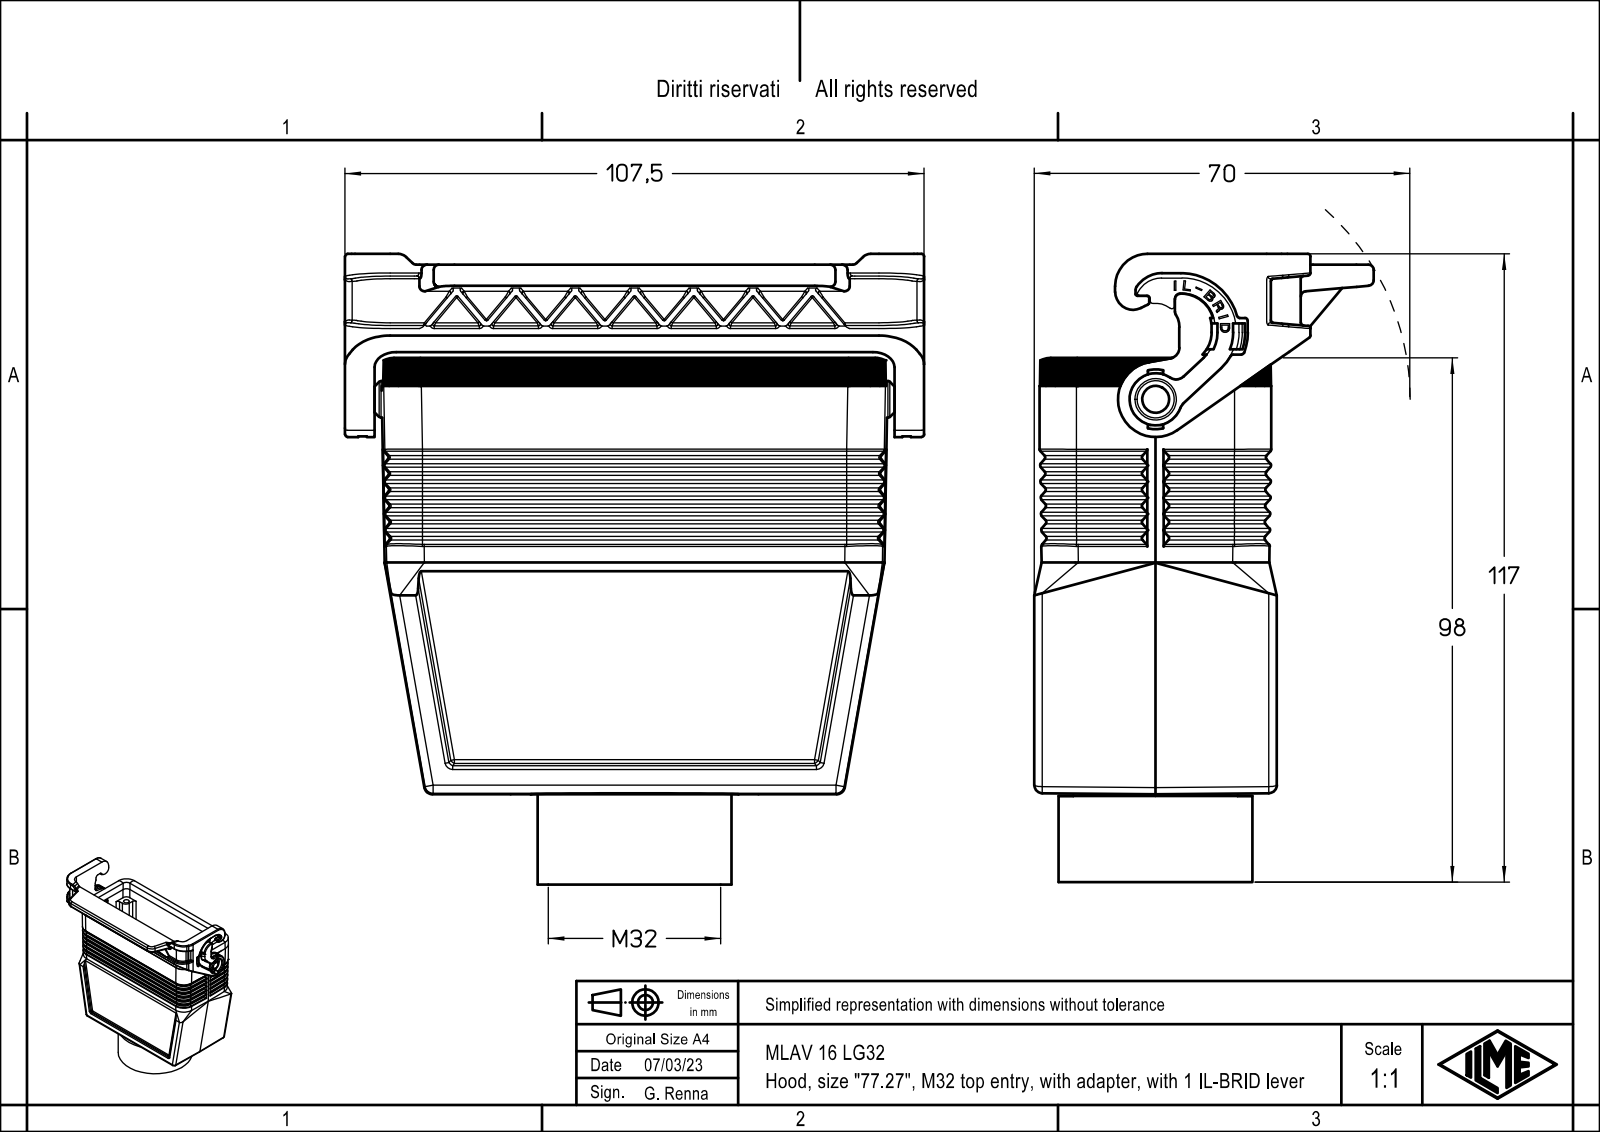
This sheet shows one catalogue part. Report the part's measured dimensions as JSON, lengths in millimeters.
{"part_name": "MLAV 16 LG40; MLAV 16 LG32", "step_written_by": "Creo Elements/Direct Modeling 20.1B 02-Apr-2019 (C) Parametric Technology GmbH (AUTOMOTIVE_DESIGN)", "units": "millimeters", "bodies": {"solids": 1, "faces": 1357, "planar": 785, "cylindrical": 370, "other": 202}, "overall_size": [119.25, 107.5, 63], "volume_mm3": 120101, "surface_area_mm2": 63125, "round_holes": [[3, 4], [3.5, 4], [3.25, 1], [5.4, 1], [7.7, 1], [30.5, 1]], "round_bosses_or_shafts": [[40, 1], [32, 1], [6.9, 1], [6.8, 1], [5.2, 1], [3.2, 1]], "partial_cylinders_radius": [[0.5, 77], [0.1, 27], [1.5, 23], [0.2, 15], [1, 15], [7, 14], [0.33, 13], [0.55, 12]], "face_to_face_distances": [3.75, 39.25, 35.5, 43, 2, 7, 46.25, 3.25, 42.5, 1], "hole_center_spacings": [41.03, 27, 77.5, 82.07]}
